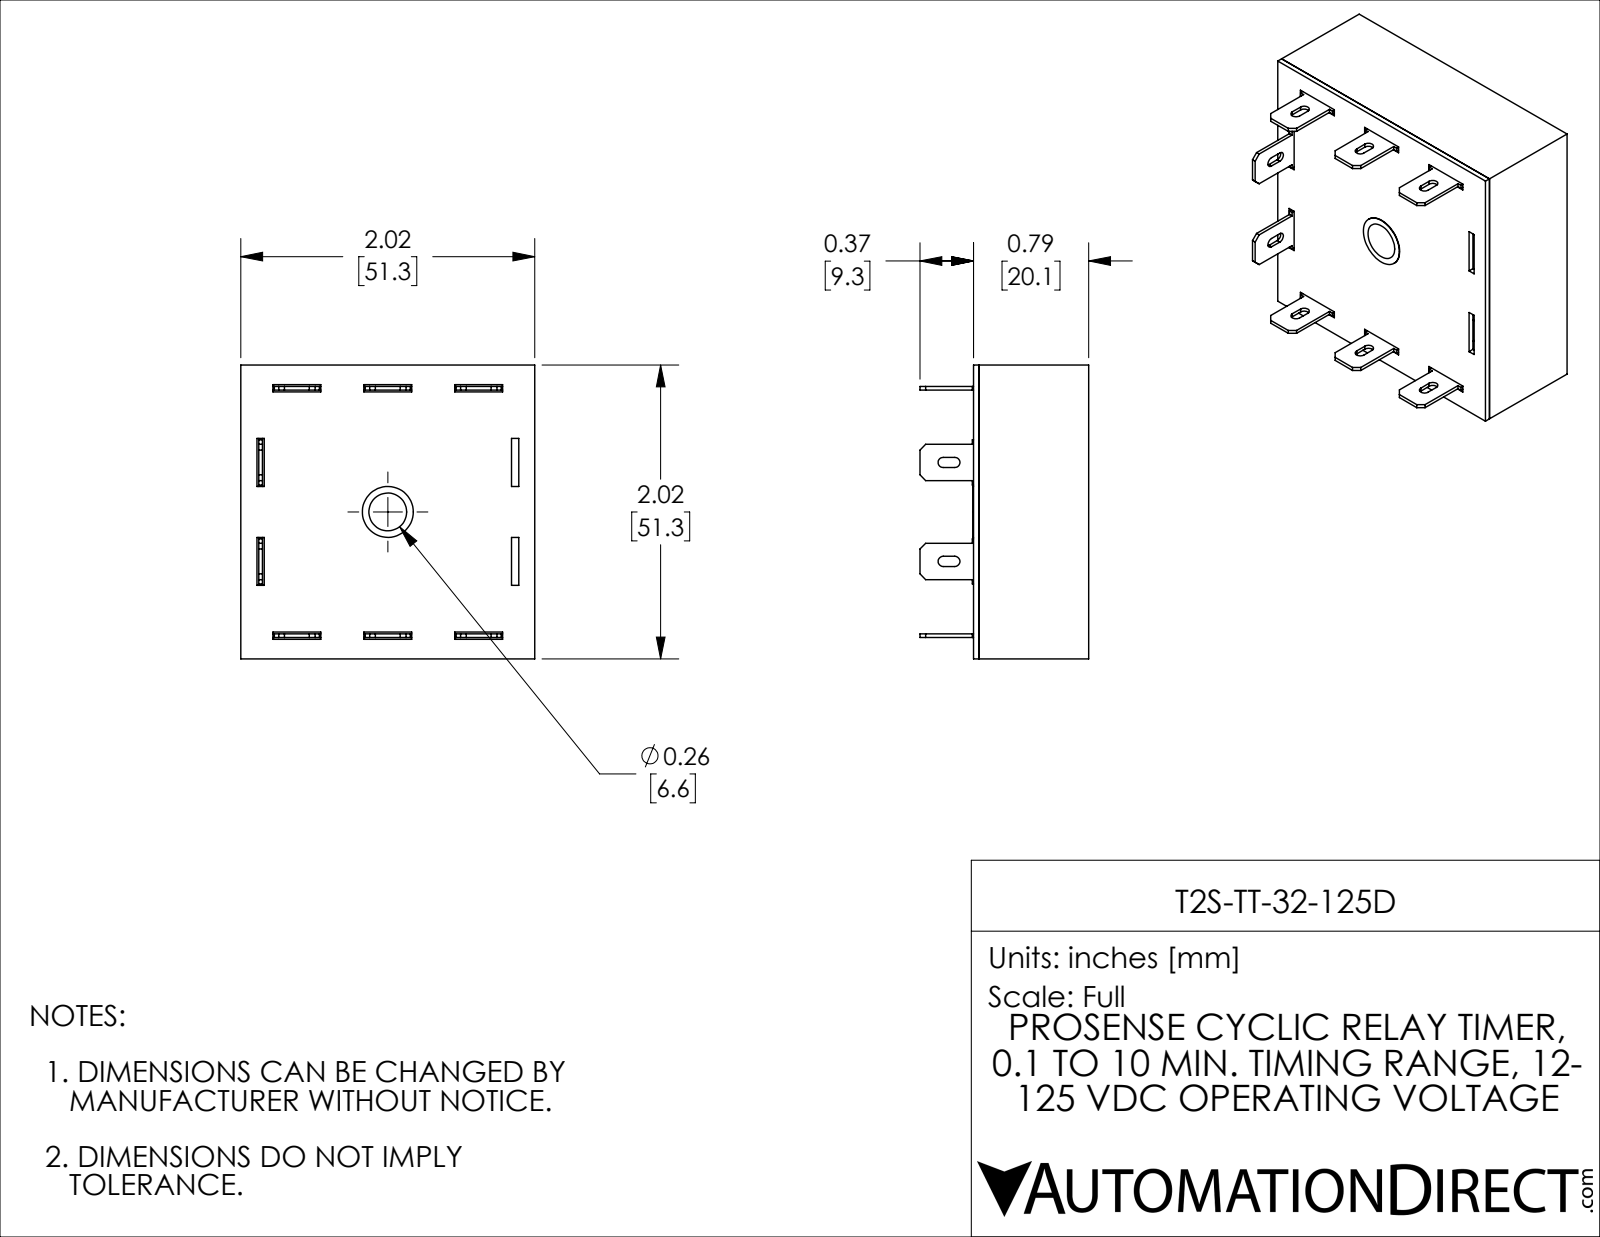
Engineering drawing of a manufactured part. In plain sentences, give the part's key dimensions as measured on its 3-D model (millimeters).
The part is named "T2S-TT-32-125D". Its 3-D file was written by "SolidWorks 2021 (CONFIG_CONTROL_DESIGN)". It is 10 solids with 256 faces: 234 planar, 20 cylindrical and 2 other. Overall it measures 51.31 by 51.31 by 29.46 millimeters. Its volume is 11 042 cubic millimeters and its surface area 22 819 square millimeters. Round holes: 1 of diameter 8.89. Partial cylindrical surfaces (rounded edges, fillets, slot ends): 10 of radius 0.89. The main face-to-face distances are 1.14, 50.16, 19.15, 20.12, 0.97, 18.01, 18.98, 51.3, 49.02, 3.74.
